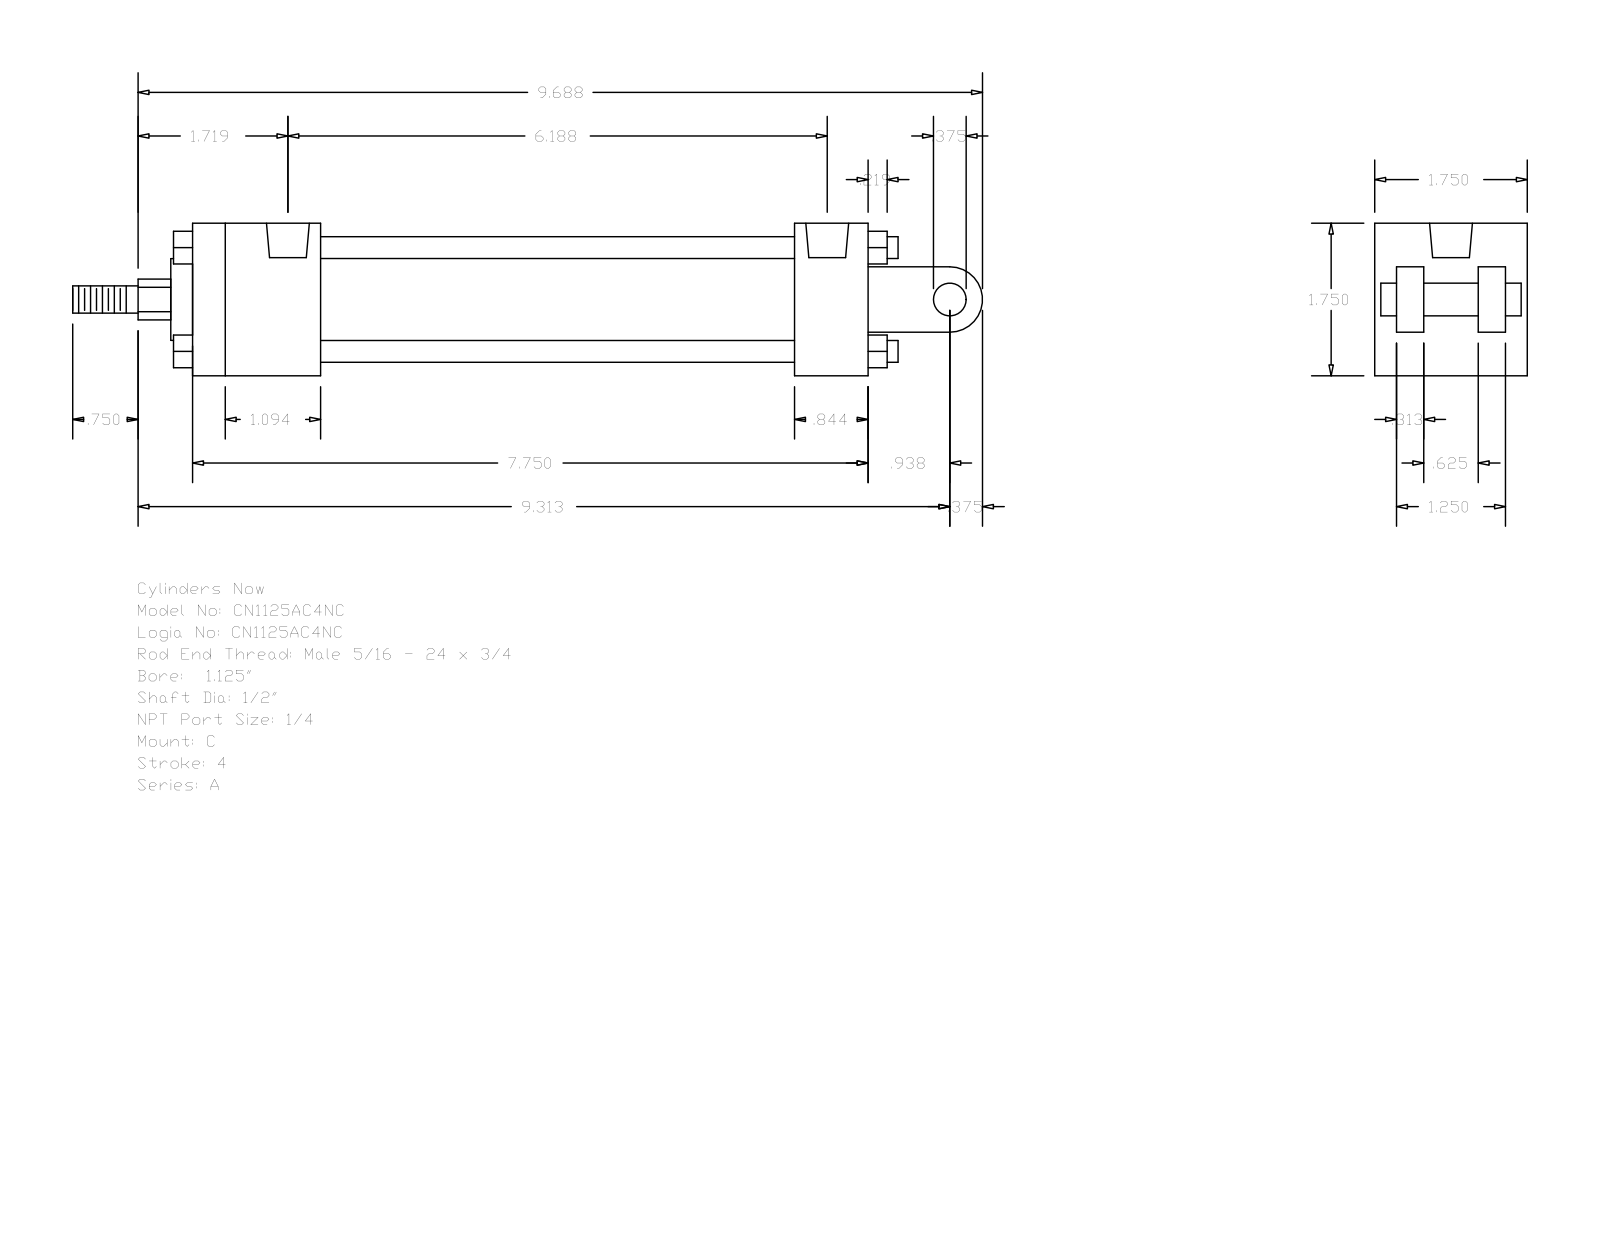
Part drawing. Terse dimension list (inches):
name: A_C__0112_0.5
written by: GSSL Pune (CONFIG_CONTROL_DESIGN)
unit: in
bodies: 0 solids, 135 faces (102 planar, 33 cylindrical, 0 other)
size: 10.437 × 1.75 × 1.75
holes: 4× ⌀0.219, 2× ⌀0.492
bosses: 4× ⌀0.25, 1× ⌀1.255, 1× ⌀0.937, 1× ⌀0.5, 1× ⌀0.375, 1× ⌀0.313
rounds: 1× R0.234, 1× R0.375
face distances: 1.75, 0.25, 1.25, 0.563, 7.75, 1.188, 6.906, 0.844, 1.469, 5.437
hole spacings: 6.063, 0.062, 0.063, 6.125, 6.125, 6.187
